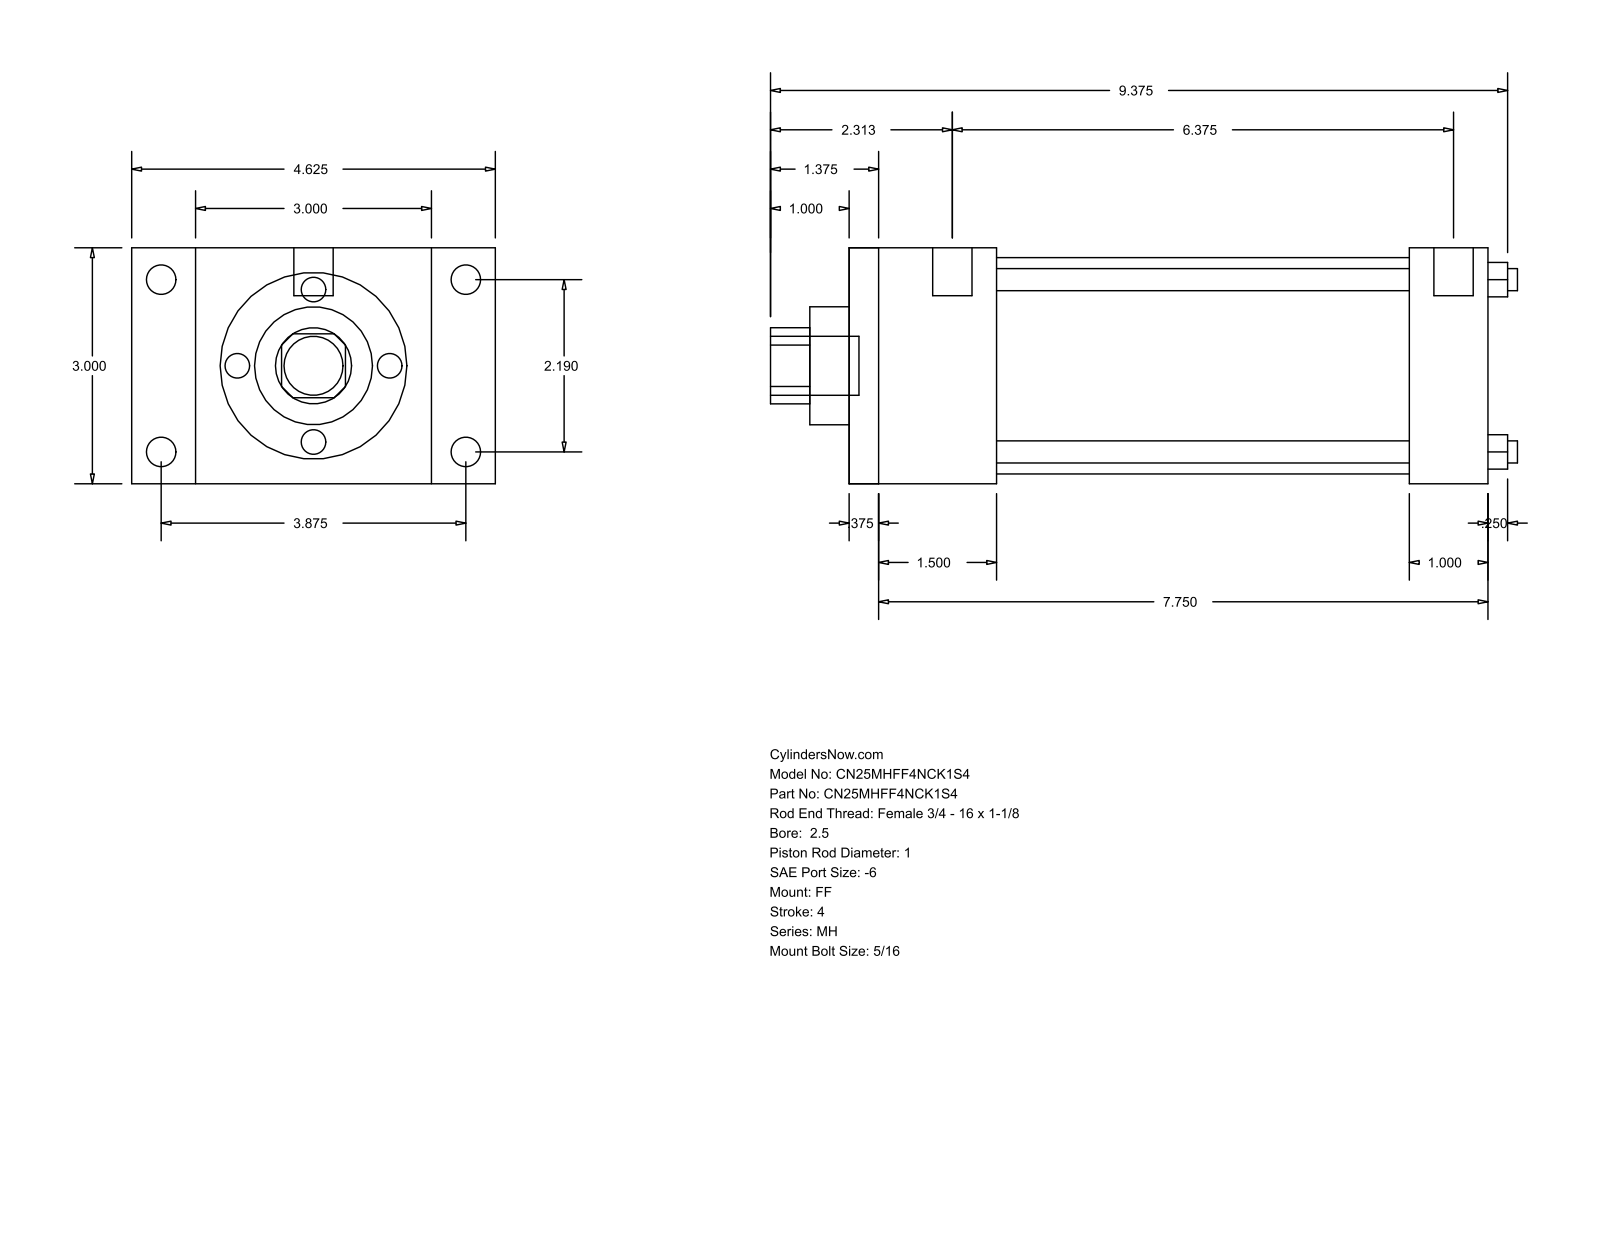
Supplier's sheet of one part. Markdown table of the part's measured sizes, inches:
| quantity | value |
| --- | --- |
| part name | MH_FF__0250_1 |
| STEP written by | GSSL Pune (CONFIG_CONTROL_DESIGN) |
| units | inches |
| bodies | 0 solids, 92 faces (64 planar, 28 cylindrical, 0 other) |
| overall size | 9.5 × 4.625 × 3 |
| round holes (diameter × count) | 0.281 × 4, 1 × 1, 1.5 × 1, 2.75 × 1 |
| round bosses / shafts (diameter × count) | 0.375 × 4, 0.219 × 4, 0.5 × 2, 0.75 × 1 |
| partial cylindrical surfaces (radius × count) | 0.484 × 1 |
| main face-to-face distances | 3, 8.125, 0.375, 7.75, 1, 1.875, 7.125, 1.5, 6.75, 5.25 |
| hole center spacings | 1.548, 2.19, 3.097 |
